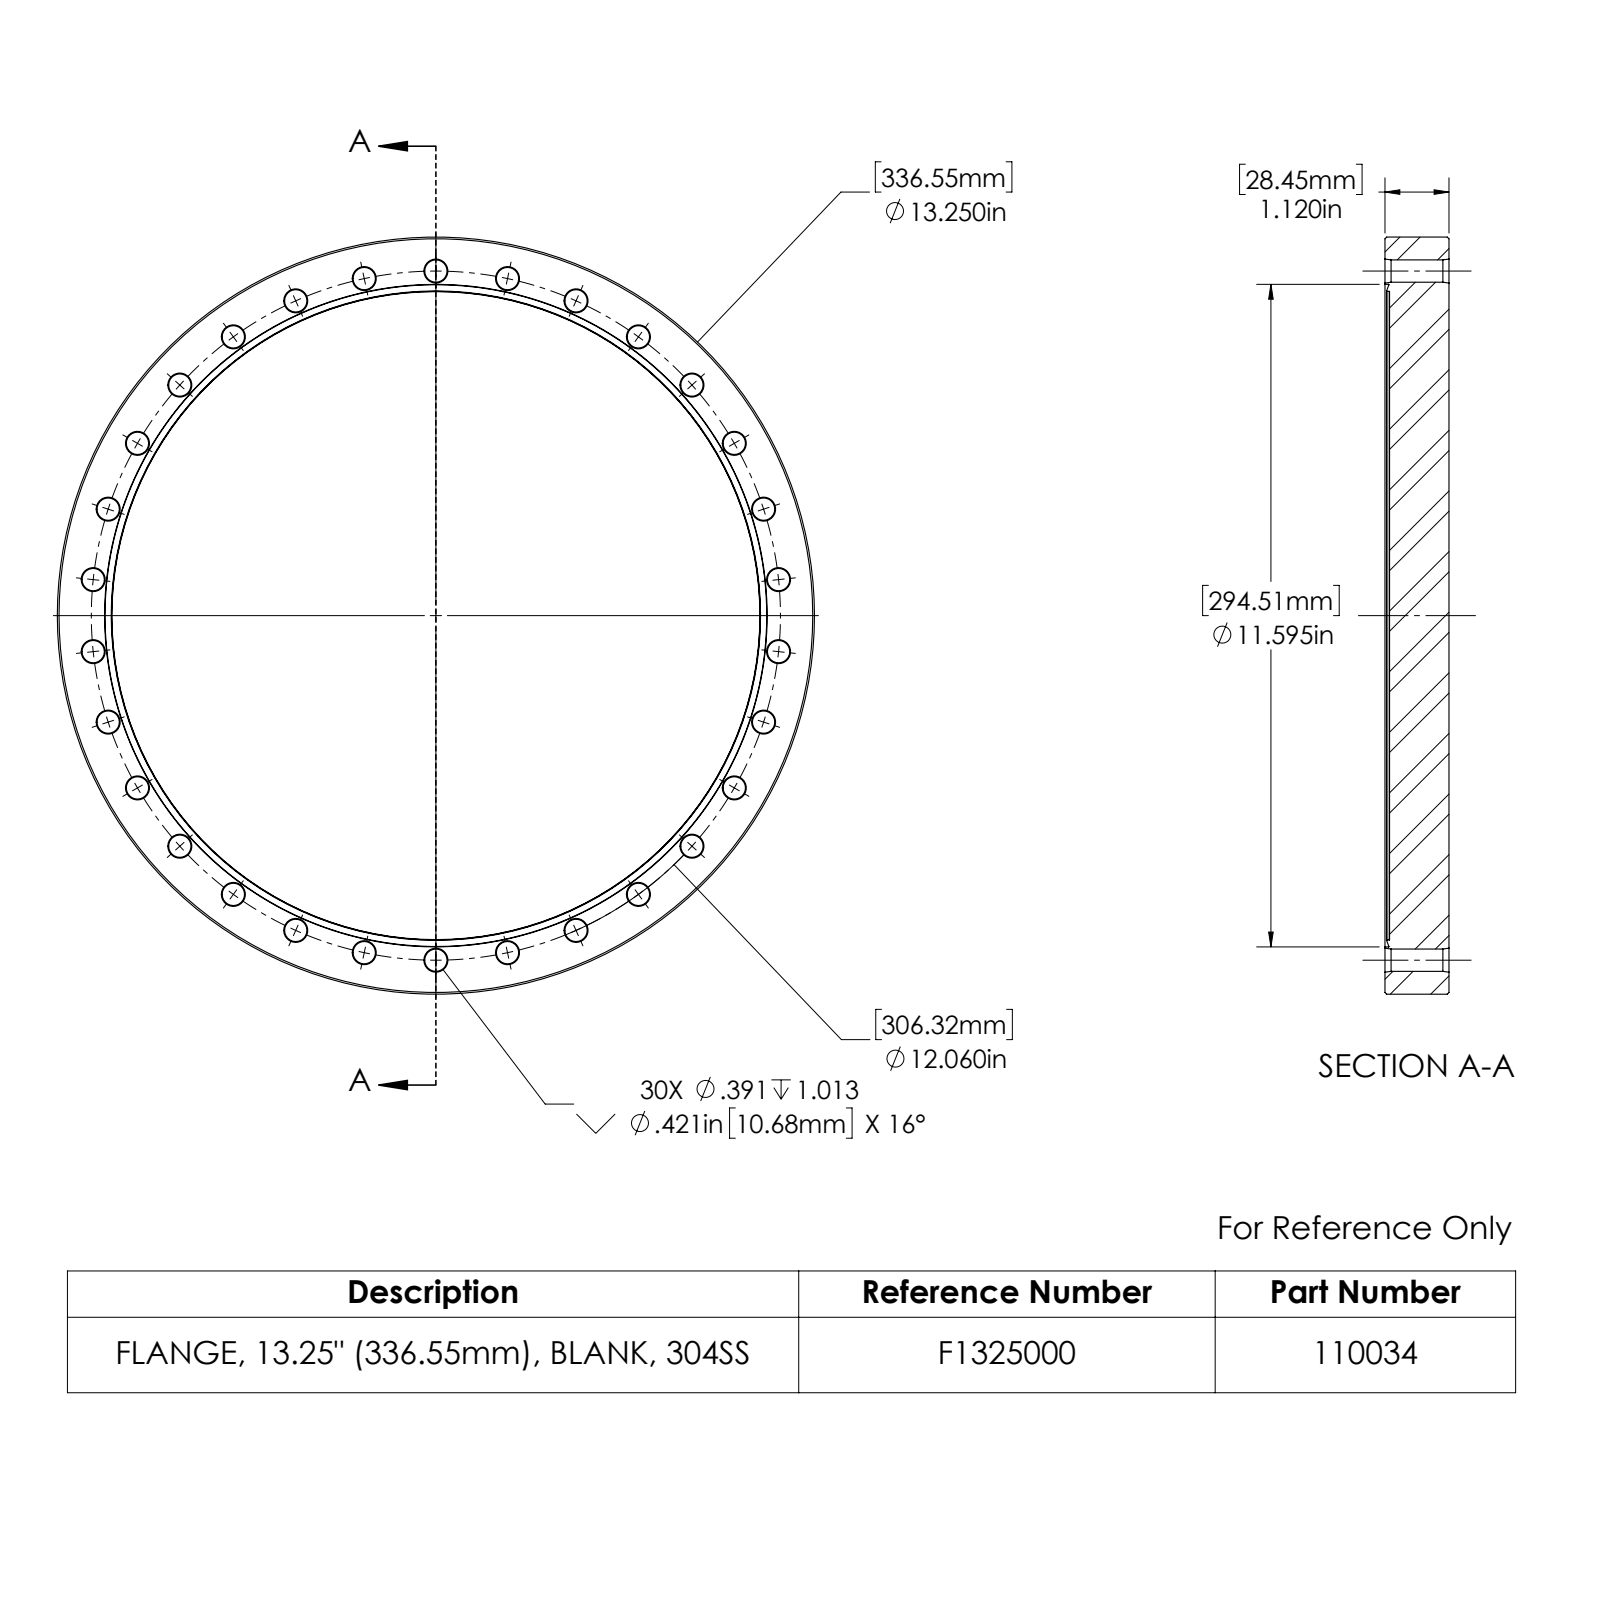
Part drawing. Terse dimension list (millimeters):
name: 110034
written by: SolidWorks 2022 (AUTOMOTIVE_DESIGN)
unit: mm
bodies: 1 solid, 201 faces (3 planar, 66 cylindrical, 132 other)
size: 336.6 × 336.6 × 28.4
volume: 2 327 000 mm³; area: 231 400 mm²
holes: 30× ⌀9.9, 1× ⌀288.3, 1× ⌀294.5
bosses: 1× ⌀336.6
face distances: 26.4, 2, 28.4
hole spacings: 94.7, 304.6, 205, 299.6, 247.8, 279.8, 124.6, 180.1
